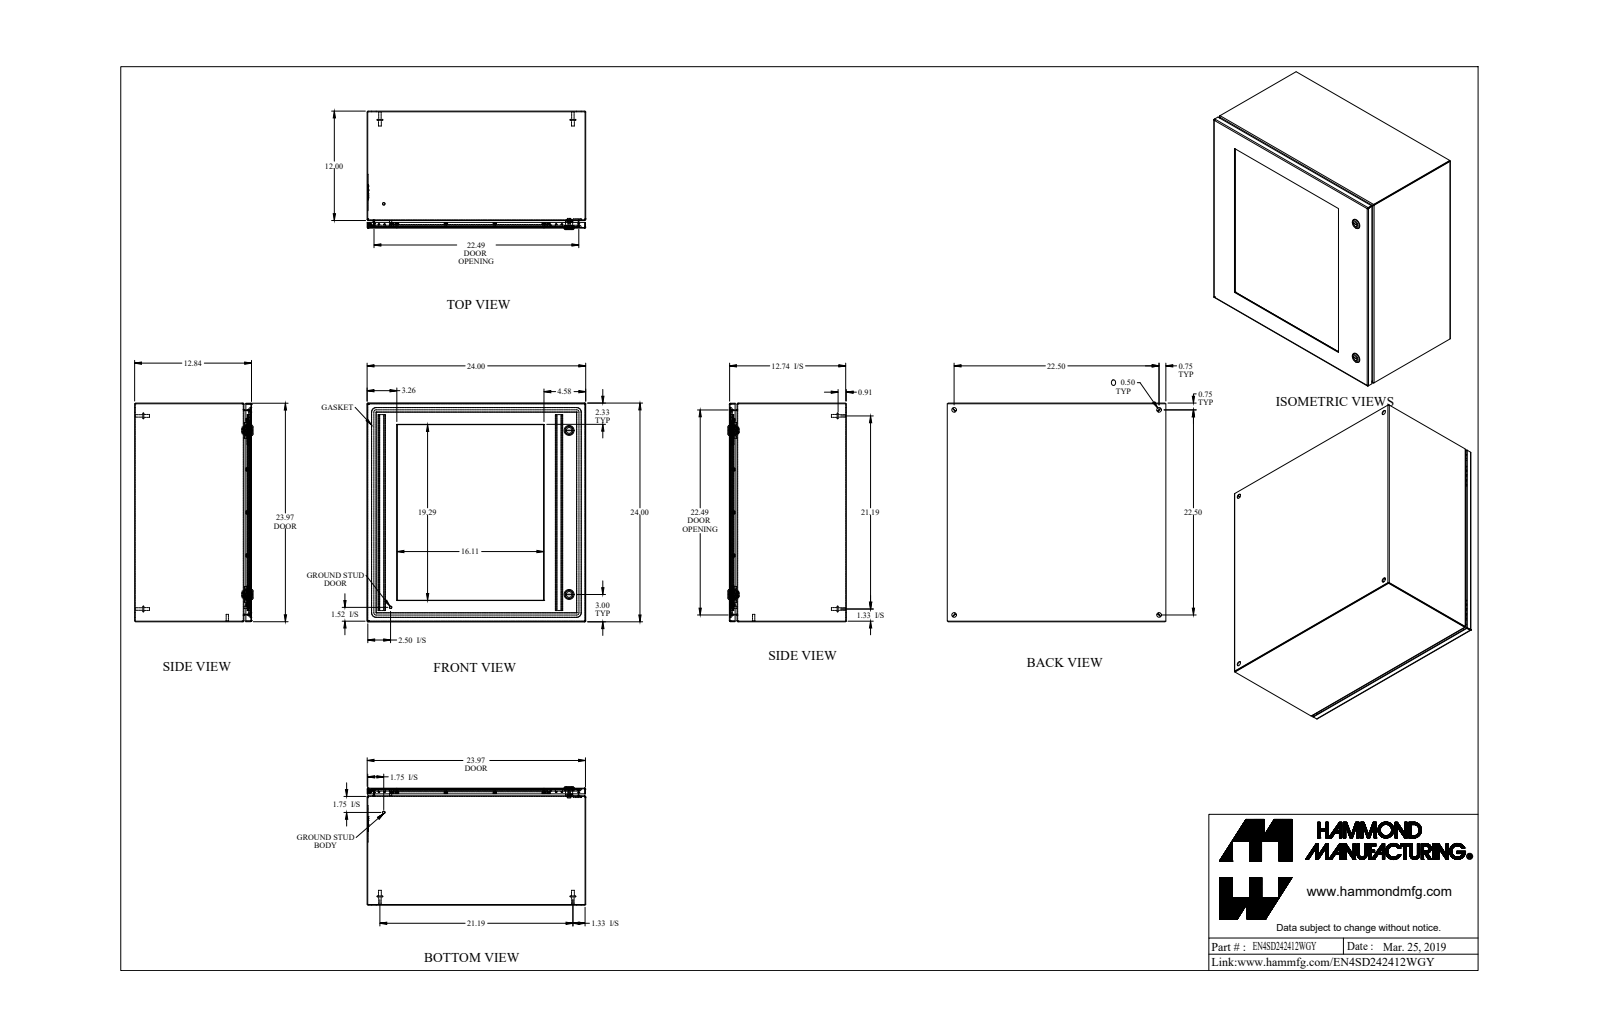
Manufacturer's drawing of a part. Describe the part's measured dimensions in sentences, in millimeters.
The part is named "EN4SD242412WGY". Its 3-D file was written by "SolidWorks 2019 (AUTOMOTIVE_DESIGN)". It is 74 solids with 1435 faces: 740 planar, 441 cylindrical and 254 other. Overall it measures 609.6 by 609.6 by 330.1 millimeters. Its volume is 4 230 000 cubic millimeters and its surface area 3 648 000 square millimeters. Round holes: 18 of diameter 3.3, 18 of diameter 6.4, 4 of diameter 12.7, 2 of diameter 5.9, 2 of diameter 15.9, 2 of diameter 19.9, 1 of diameter 4.4, 1 of diameter 6.1, 1 of diameter 6.1. Round bosses or shafts: 19 of diameter 5.7, 18 of diameter 9.3, 18 of diameter 4.2, 4 of diameter 15.9, 4 of diameter 8, 4 of diameter 6.9, 2 of diameter 27.9, 2 of diameter 13.3. Partial cylindrical surfaces (rounded edges, fillets, slot ends): 14 of radius 0.9, 14 of radius 2.7, 12 of radius 1.1, 12 of radius 2.1, 12 of radius 3.2, 12 of radius 7.9, 8 of radius 2.5, 4 of radius 0.2. The main face-to-face distances are 1.8, 607.8, 324.2, 322.4, 605.9, 609.6, 316.1, 6.4, 317.9, 8.2. The hole center spacings are 136.4, 451.6, 119.9, 497.1, 534.2, 136.4, 239.7, 272.9.
